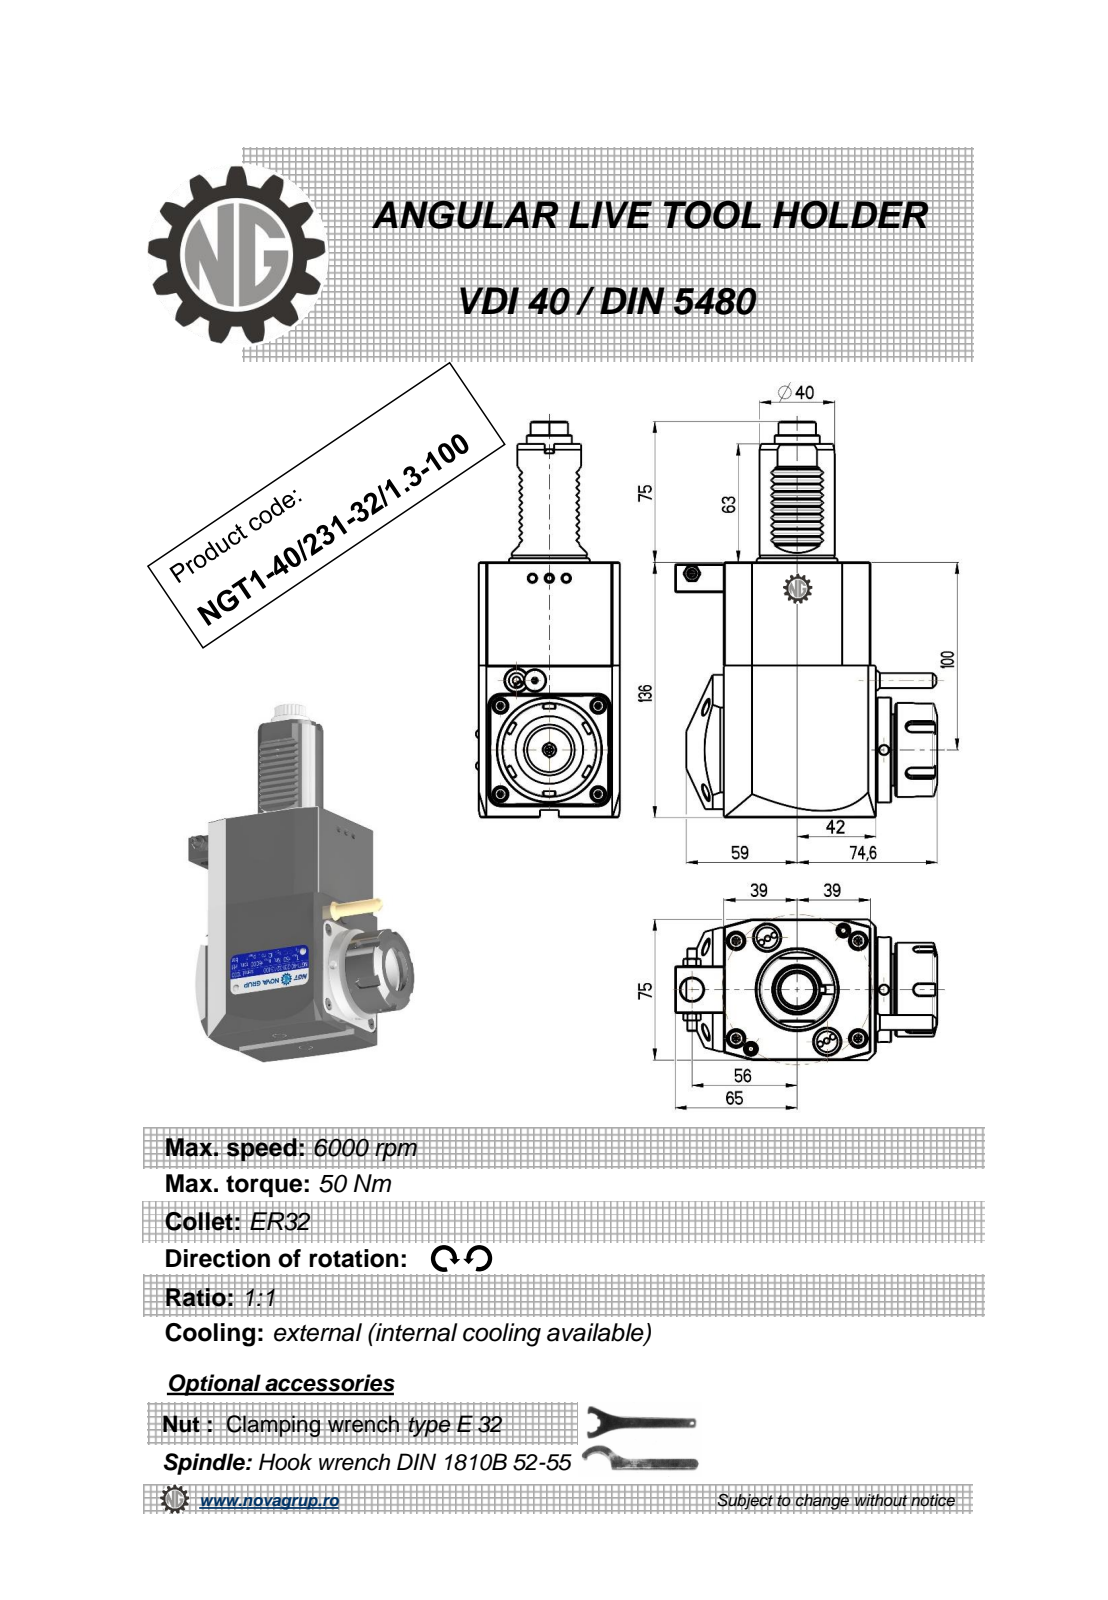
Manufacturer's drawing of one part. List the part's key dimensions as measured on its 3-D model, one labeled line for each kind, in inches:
Part name (STEP PRODUCT): NGT1_40_231_32_1_3_100
STEP written by: PRO/ENGINEER BY PARAMETRIC TECHNOLOGY CORPORATION, 2010280 (CONFIG_CONTROL_DESIGN)
Units: inches
Bodies: 1 solid, 583 faces (229 planar, 191 cylindrical, 163 other)
Overall size (bounding box): 8.307 × 5.496 × 2.953
Volume: 60.78 in³ · Surface area: 120.2 in²
Round holes (diameter × count): ⌀0.197 ×3, ⌀0.118 ×1, ⌀0.165 ×1, ⌀0.374 ×1, ⌀0.472 ×1, ⌀1.063 ×1
Round bosses / shafts (diameter × count): ⌀2.205 ×1, ⌀1.969 ×1, ⌀1.693 ×1, ⌀1.575 ×1, ⌀0.945 ×1, ⌀0.441 ×1, ⌀0.353 ×1, ⌀0.315 ×1
Partial cylindrical surfaces — rounded edges, fillets, slot ends (radius × count): R0.082 ×48, R0.012 ×20, R0.01 ×12, R0.009 ×6, R0.118 ×5, R0.357 ×1, R0.391 ×1, R0.591 ×1
Main face-to-face distances: 2.953, 5.354, 3.071, 3.189, 0.118, 3.342, 0.295, 3.181, 0.11, 0.02
Hole centre spacings: 1.611, 2.254, 3.602, 4.026, 5.468
